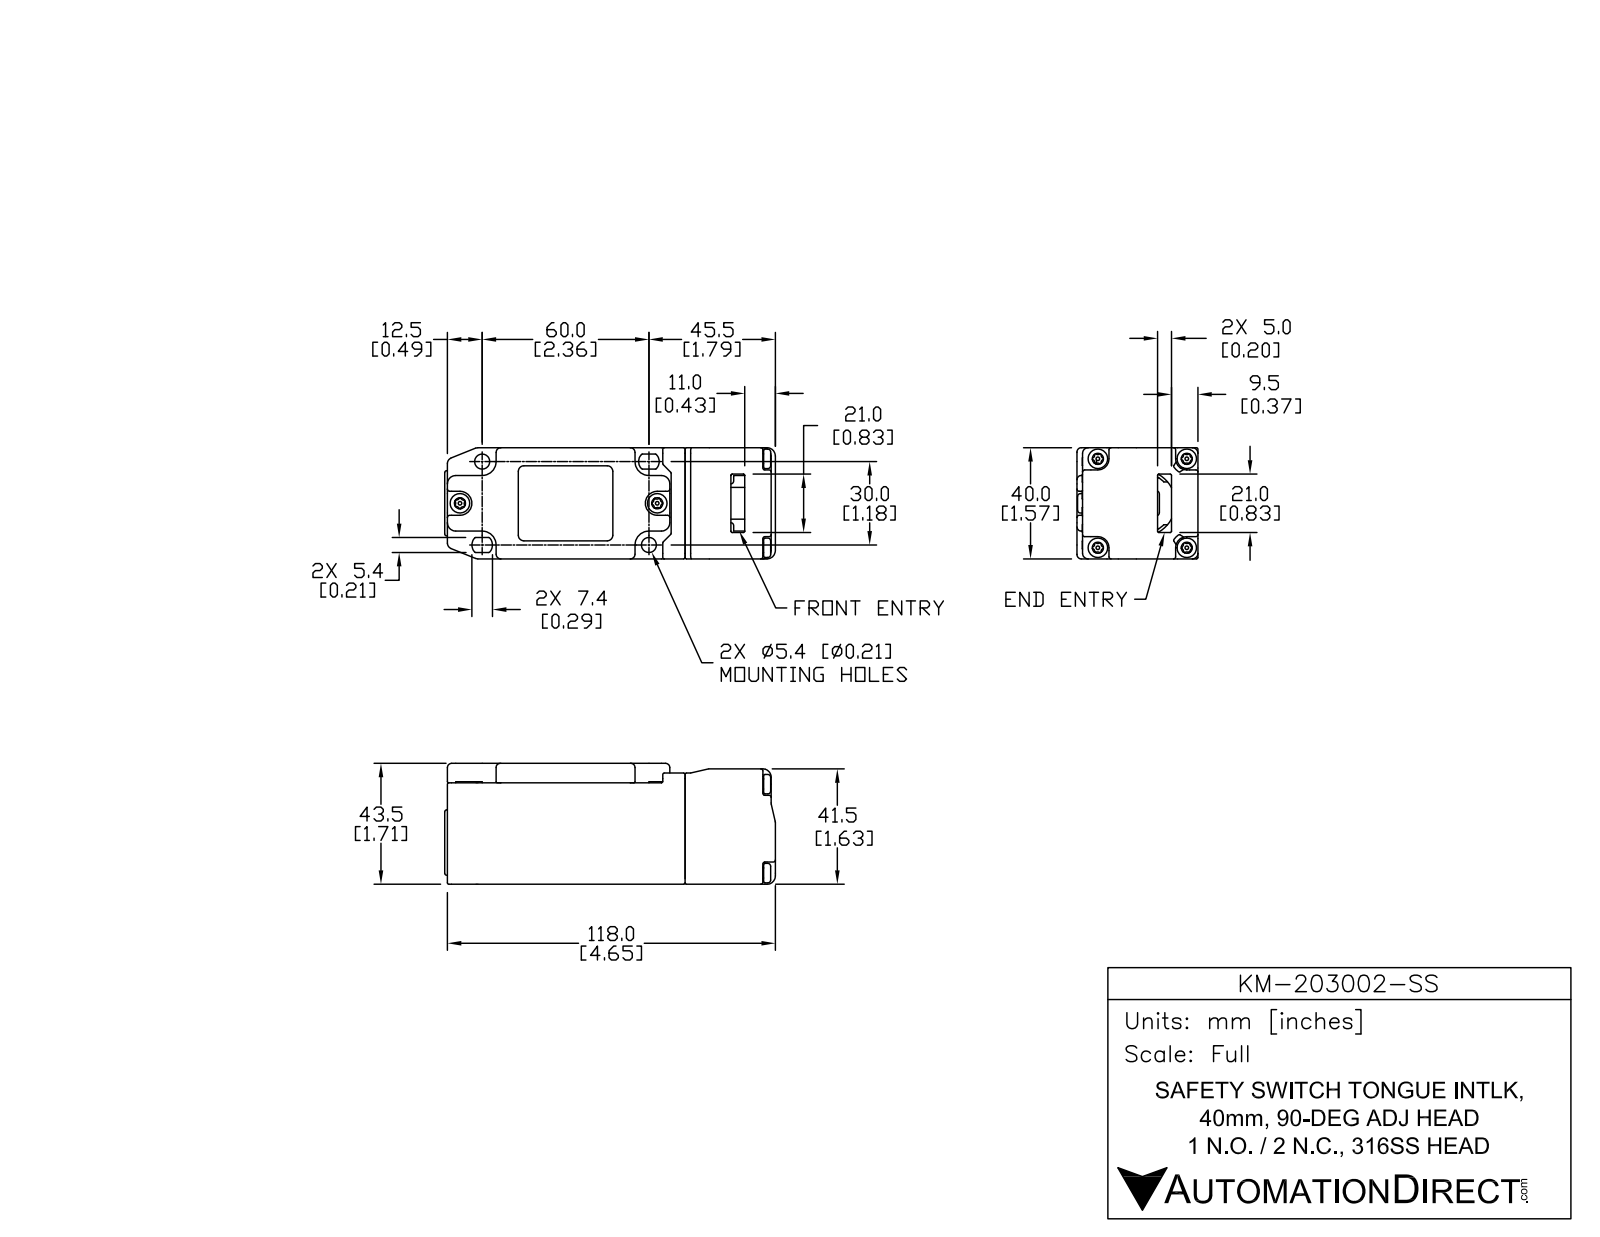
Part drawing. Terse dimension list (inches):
name: KM-203002-SS
written by: SolidWorks 2013 (AUTOMOTIVE_DESIGN)
unit: in
bodies: 1 solid, 581 faces (128 planar, 263 cylindrical, 190 other)
size: 4.71 × 1.715 × 1.575
volume: 11.19 in³; area: 44.12 in²
holes: 2× ⌀0.213
bosses: 4× ⌀0.267, 2× ⌀0.261, 1× ⌀0.906, 1× ⌀0.22
rounds: 95× R0.02, 68× R0.01, 5× R0.118, 4× R0.057, 4× R0.067, 4× R0.108, 4× R0.157, 4× R0.197
face distances: 1.575, 1.713, 0.02, 1.693, 4.646, 0.102, 0.197, 0.374, 4.016, 0.63
hole spacings: 2.641
